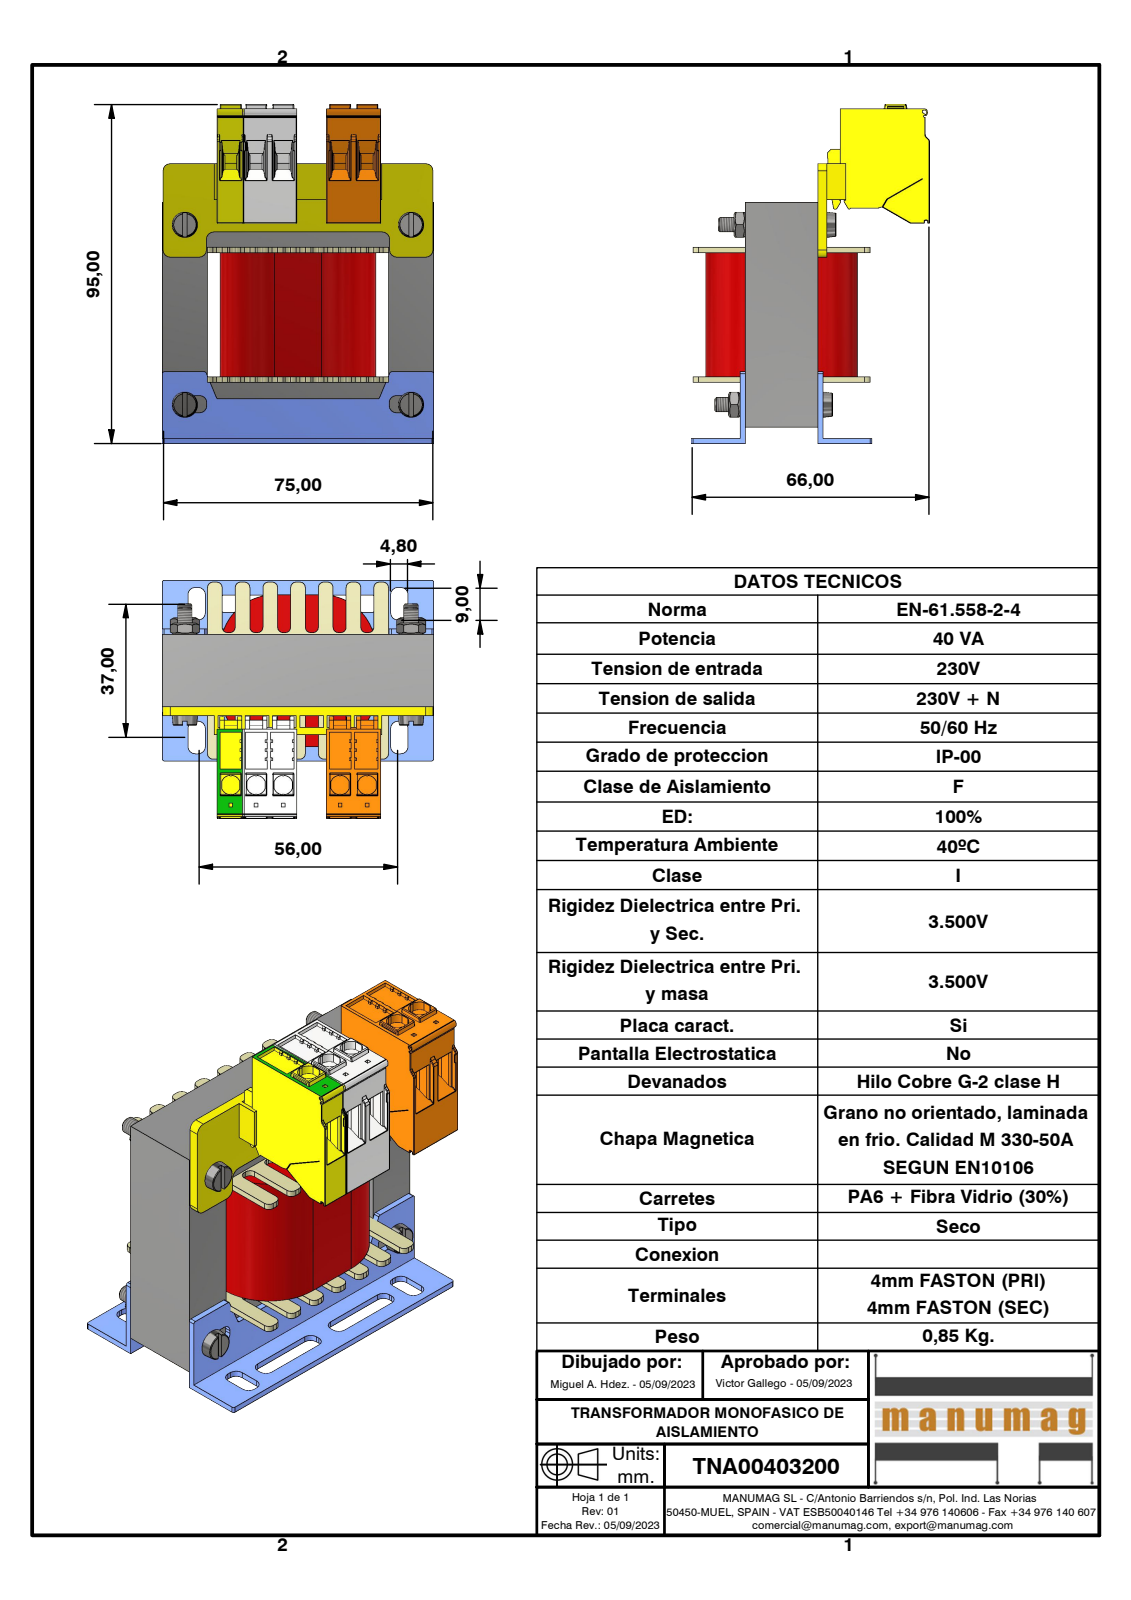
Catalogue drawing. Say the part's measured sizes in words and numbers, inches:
The part is named "TNA00403200; EI75 x 62,5 - 20 (RC25); AF25DIN; DIN 934 - M4 x 0,7 (+6 more)". Its 3-D file was written by "Autodesk Inventor 2023 (AUTOMOTIVE_DESIGN)". It is 16 solids with 5231 faces: 4283 planar, 664 cylindrical and 284 other. Overall it measures 3.715 by 2.953 by 2.596 inches. Its volume is 9.11 cubic inches and its surface area 100.3 square inches. Round holes: 4 of diameter 0.128, 4 of diameter 0.177, 2 of diameter 0.157. Round bosses or shafts: 4 of diameter 0.143, 2 of diameter 0.157. Partial cylindrical surfaces (rounded edges, fillets, slot ends): 214 of radius 0.006, 58 of radius 0.008, 52 of radius 0.059, 48 of radius 0.079, 24 of radius 0.02, 6 of radius 0.012, 6 of radius 0.197, 5 of radius 0.106. The main face-to-face distances are 0.492, 1.969, 0.787, 0.059, 0.984, 1.476, 2.461, 0.673, 2.091, 0.846. The hole center spacings are 1.969, 2.461, 3.151.
